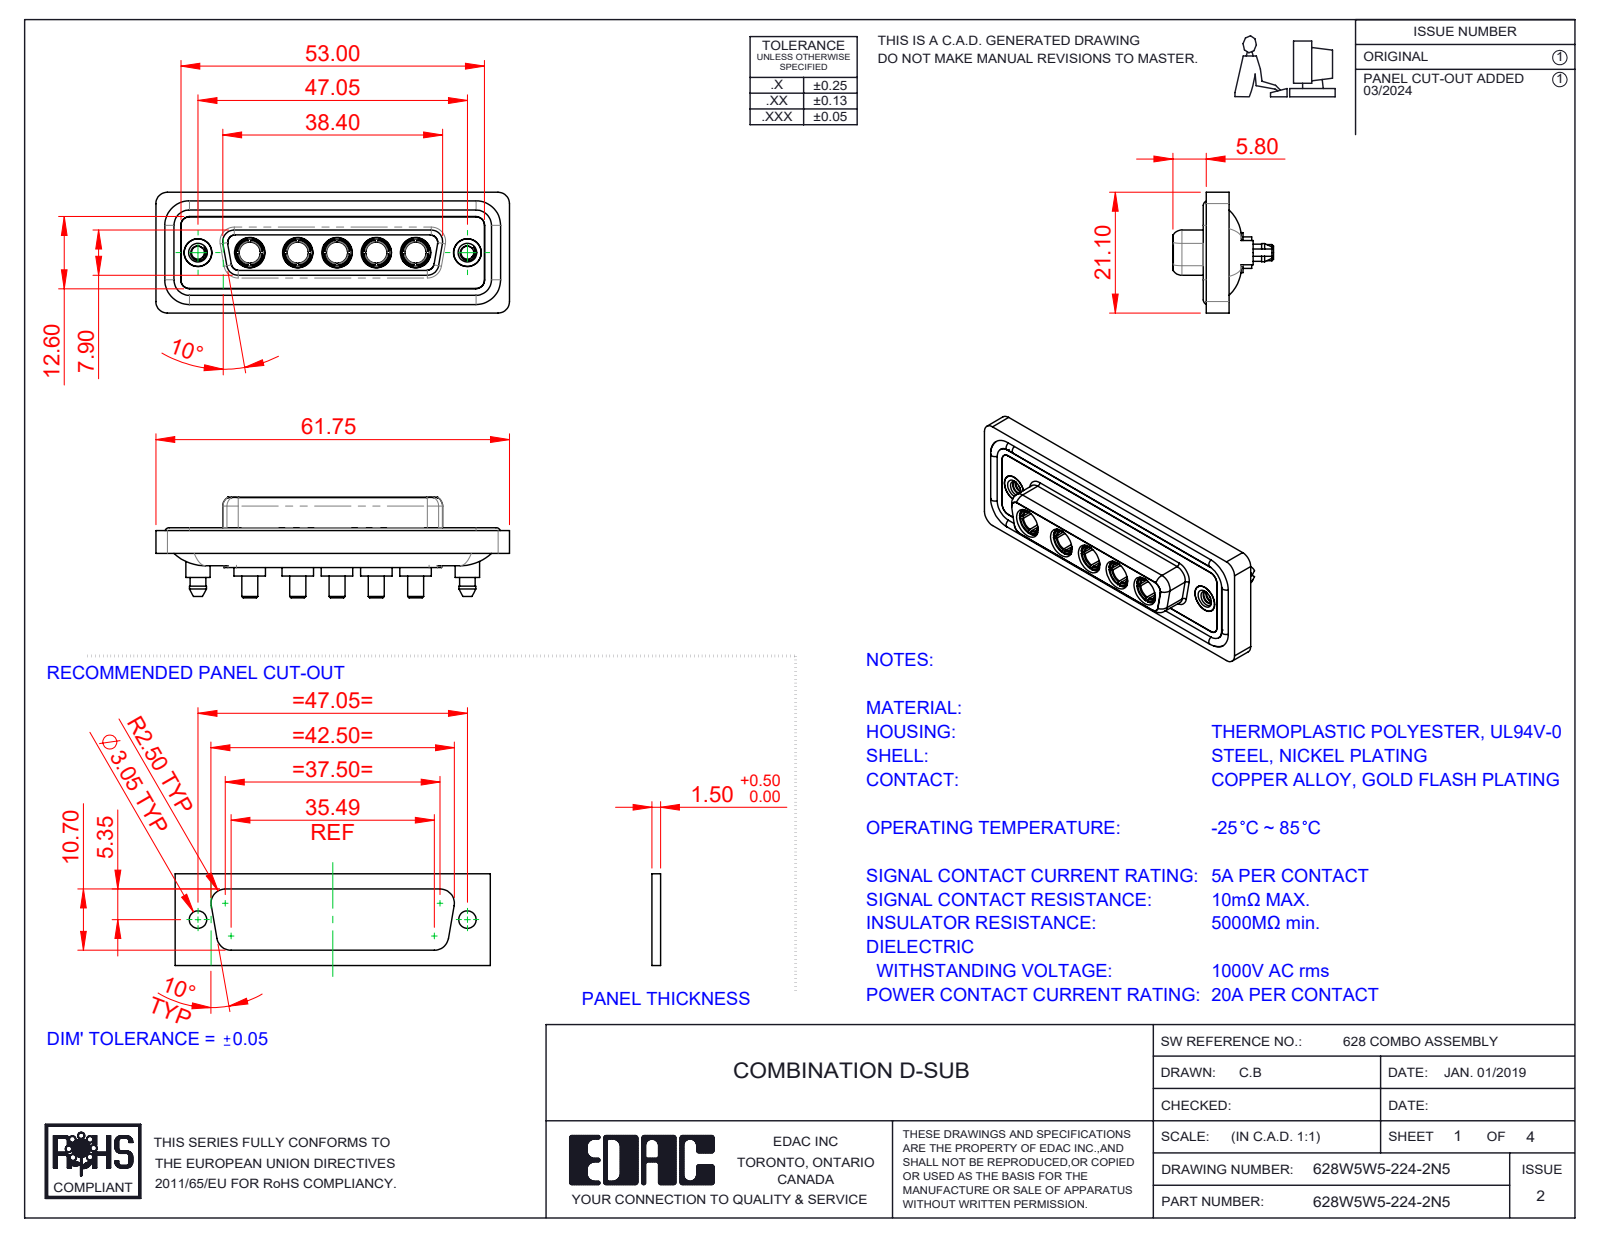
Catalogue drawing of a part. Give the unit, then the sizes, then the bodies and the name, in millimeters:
Units: millimetres
Overall size (bounding box): 61.75 × 21.1 × 17.55
Round holes (diameter × count): ⌀4.85 ×7, ⌀3.7 ×5, ⌀5.3 ×5, ⌀2.26 ×2, ⌀4 ×2, ⌀4.05 ×2, ⌀5 ×2
Round bosses / shafts (diameter × count): ⌀5.5 ×5, ⌀5.2 ×5, ⌀4.96 ×5, ⌀4.75 ×5, ⌀3.75 ×5, ⌀2.8 ×5, ⌀1.6 ×4, ⌀5.4 ×2
Partial cylindrical surfaces — rounded edges, fillets, slot ends (radius × count): R1.5 ×24, R2 ×18, R1.6 ×10, R1.35 ×8, R2.1 ×5, R0.25 ×4, R0.5 ×4, R0.6 ×4
Main face-to-face distances: 0.4, 1.8, 7.45, 5.65, 0.5, 7.05, 6.6, 1.6, 1.1, 2.9
Hole centre spacings: 6.86, 9.04, 13.72, 38.01, 8.39, 15.25, 15.9, 17.43
Volume: 8 306 mm³ · Surface area: 13 748 mm²
Bodies: 17 solids, 806 faces (266 planar, 335 cylindrical, 205 other)
Part name (STEP PRODUCT): 628Combo Threaded Boardlock_5; 628Combo Shell Front_25 Contacts; 628Combo Housing_5W5; 628Combo Waterproof Housing_25 Contacts (+3 more)
STEP written by: SolidWorks 2023 (CONFIG_CONTROL_DESIGN)
